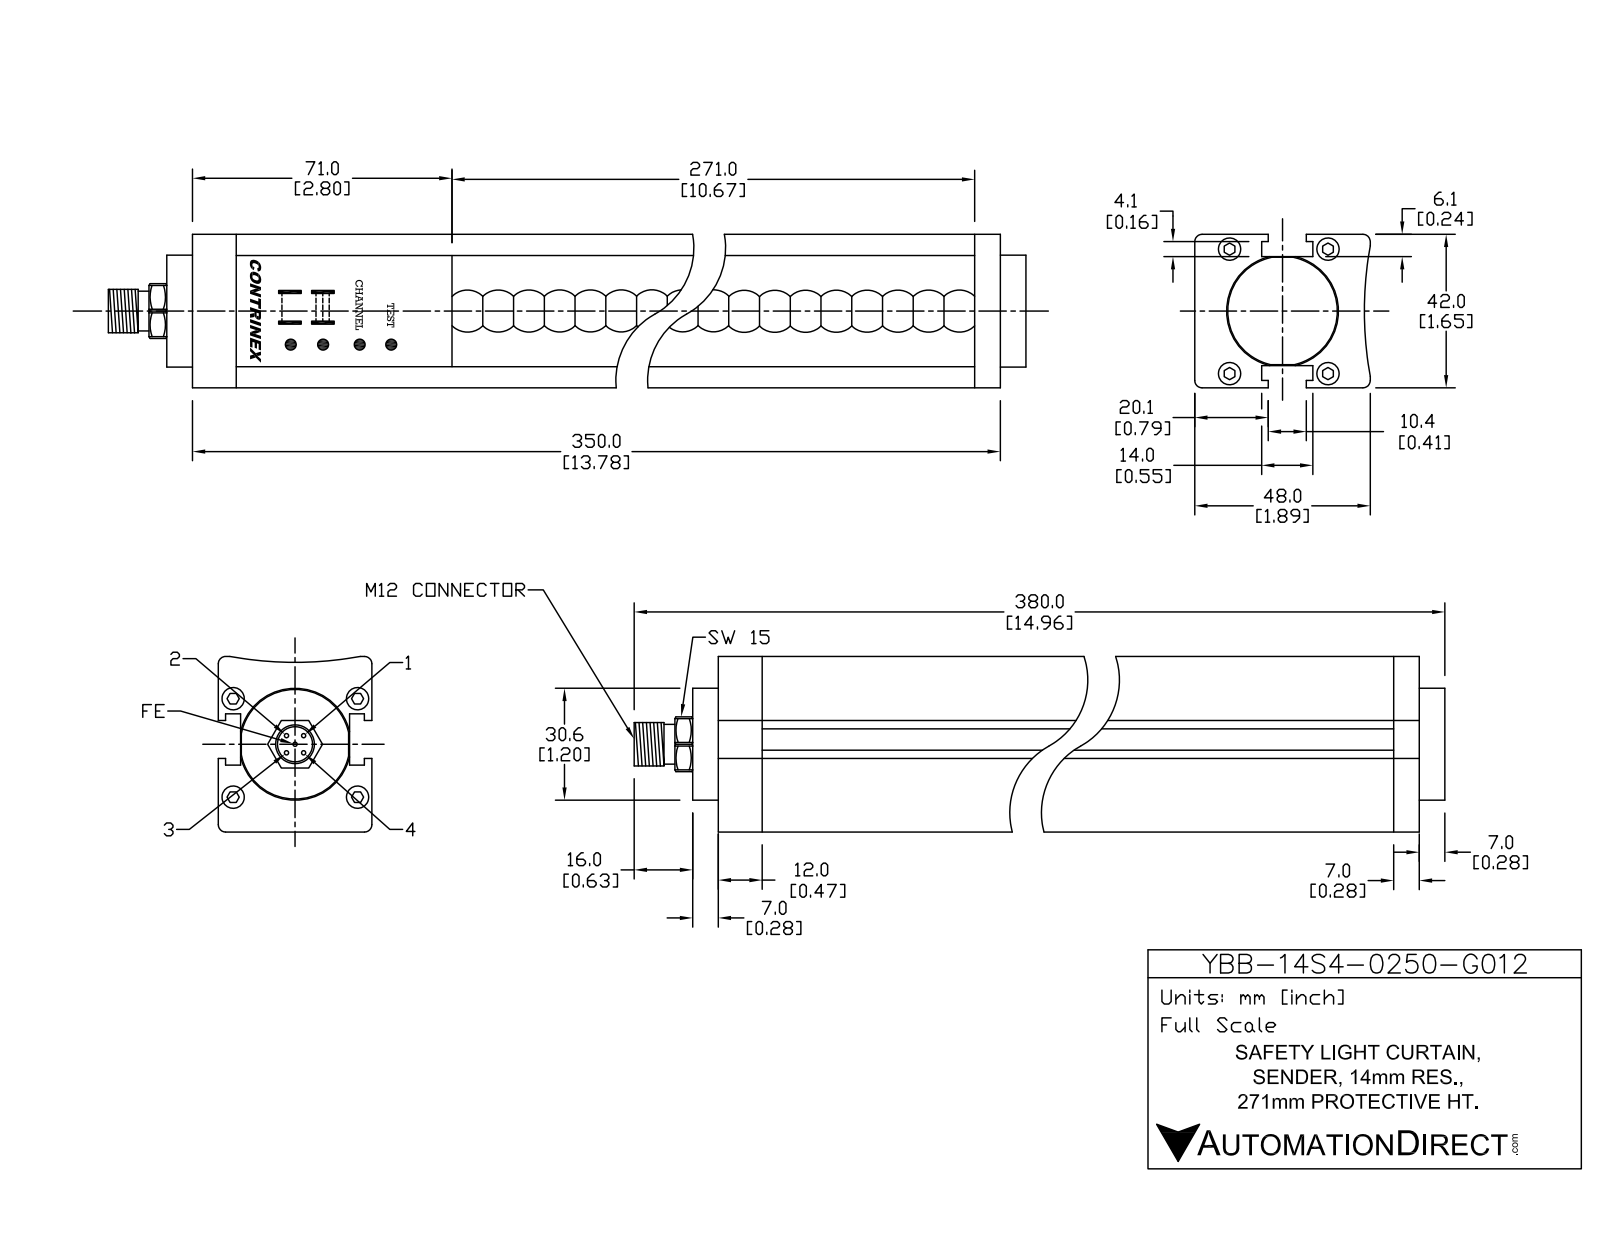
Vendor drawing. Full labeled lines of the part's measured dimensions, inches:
Part name (STEP PRODUCT): YBB-14S4-0250-G012
STEP written by: SolidWorks 2016 (AUTOMOTIVE_DESIGN)
Units: inches
Bodies: 19 solids, 440 faces (208 planar, 168 cylindrical, 64 other)
Overall size (bounding box): 14.961 × 1.89 × 1.654
Volume: 38.88 in³ · Surface area: 143.3 in²
Round holes (diameter × count): ⌀0.236 ×4, ⌀0.335 ×1, ⌀1.26 ×1
Round bosses / shafts (diameter × count): ⌀0.039 ×5, ⌀0.217 ×4, ⌀1.205 ×1, ⌀0.472 ×1, ⌀0.413 ×1
Partial cylindrical surfaces — rounded edges, fillets, slot ends (radius × count): R0.039 ×48, R0.02 ×4, R0.022 ×2, R0.323 ×1, R3.937 ×1
Main face-to-face distances: 0.248, 1.406, 1.654, 1.157, 12.992, 0.551, 0.677, 1.228, 0.315, 0.472
Hole centre spacings: 0.828, 0.88, 1.059, 1.339, 1.707
